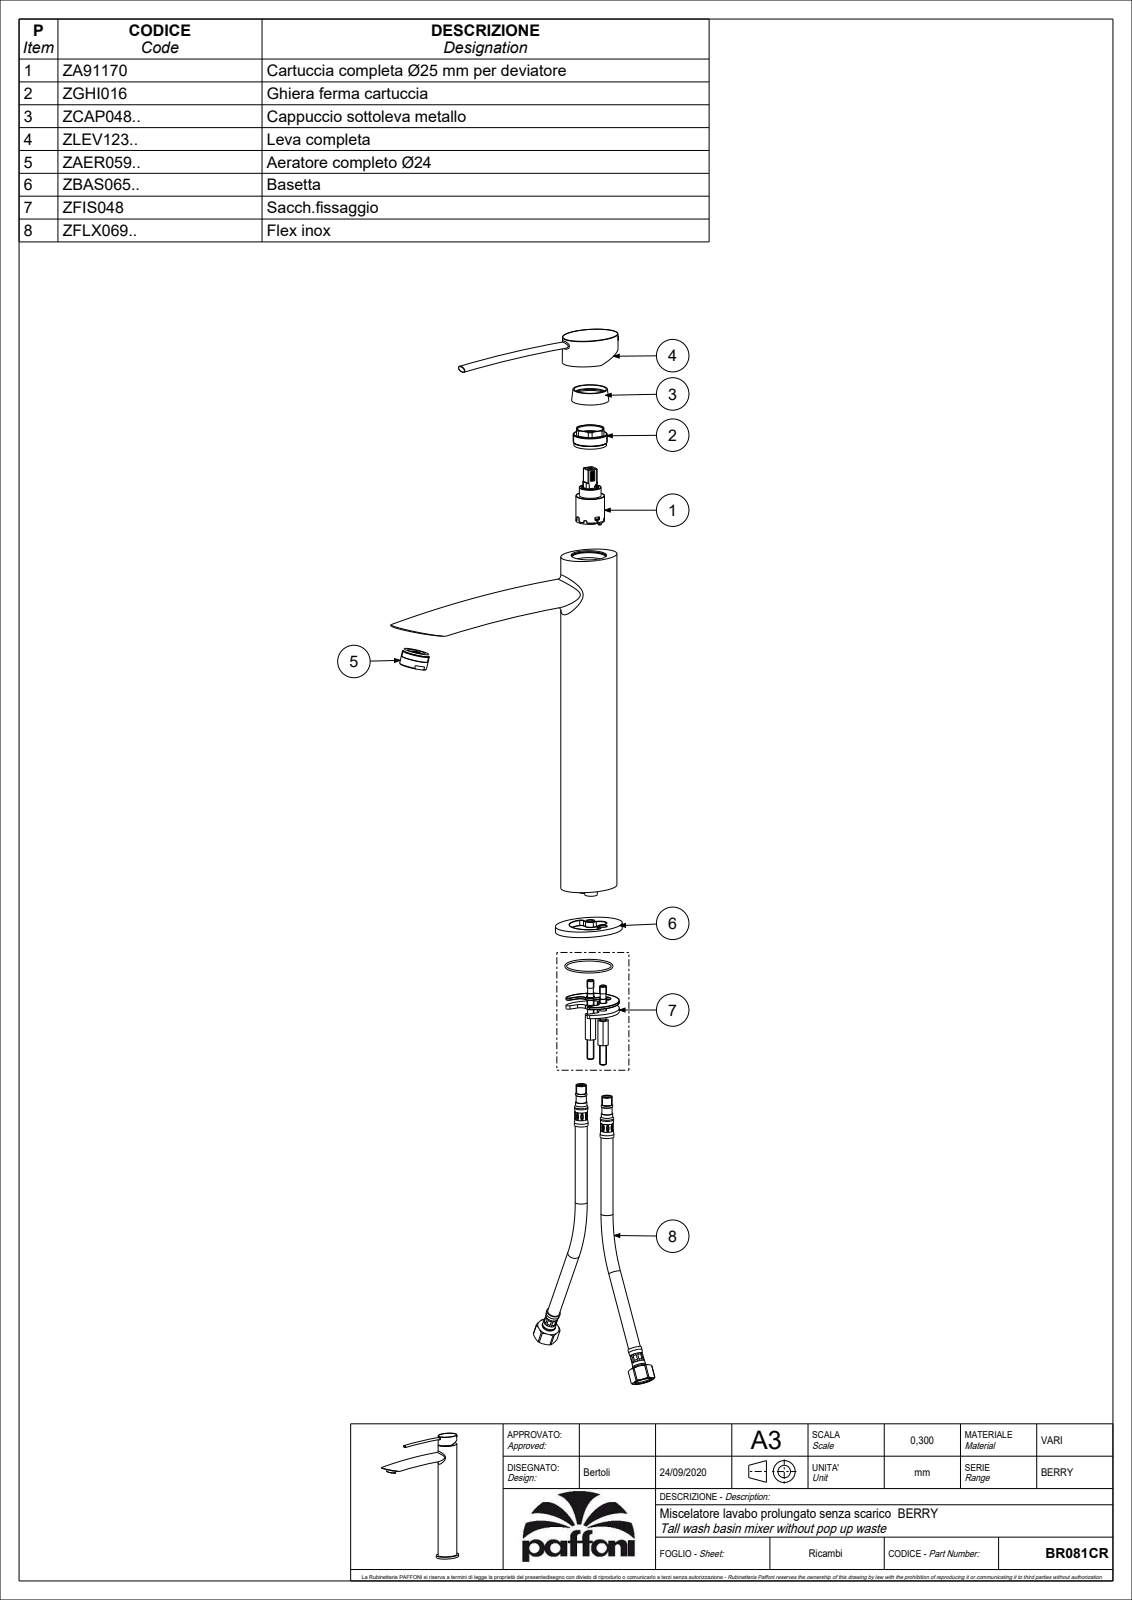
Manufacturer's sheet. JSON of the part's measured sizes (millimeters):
{"part_name": "BR081CR", "step_written_by": "CREO PARAMETRIC BY PTC INC, 2020044 (CONFIG_CONTROL_DESIGN)", "units": "millimeters", "bodies": {"solids": 2, "faces": 2624, "planar": 1949, "cylindrical": 361, "other": 314}, "overall_size": [330.2, 229.6, 46], "volume_mm3": 248678, "surface_area_mm2": 162510, "round_holes": [[5, 4], [6, 4], [3, 2], [3.2, 2], [6.2, 2], [8.2, 2], [20, 2], [4.2, 1], [7, 1], [15, 1], [16, 1], [17, 1]], "round_bosses_or_shafts": [[8, 4], [3, 2], [38.8, 1], [28.5, 1], [26, 1], [25, 1], [24, 1], [23.2, 1]], "partial_cylinders_radius": [[0.5, 52], [1, 24], [0.3, 23], [0.2, 13], [0.15, 10], [2, 10], [1.5, 4], [2.45, 4]], "face_to_face_distances": [25, 5, 1, 12, 6, 274, 7, 19, 2, 327.9], "hole_center_spacings": [3.64, 4.24, 5.59, 6.36, 6.5, 8, 8.14, 9.43]}
